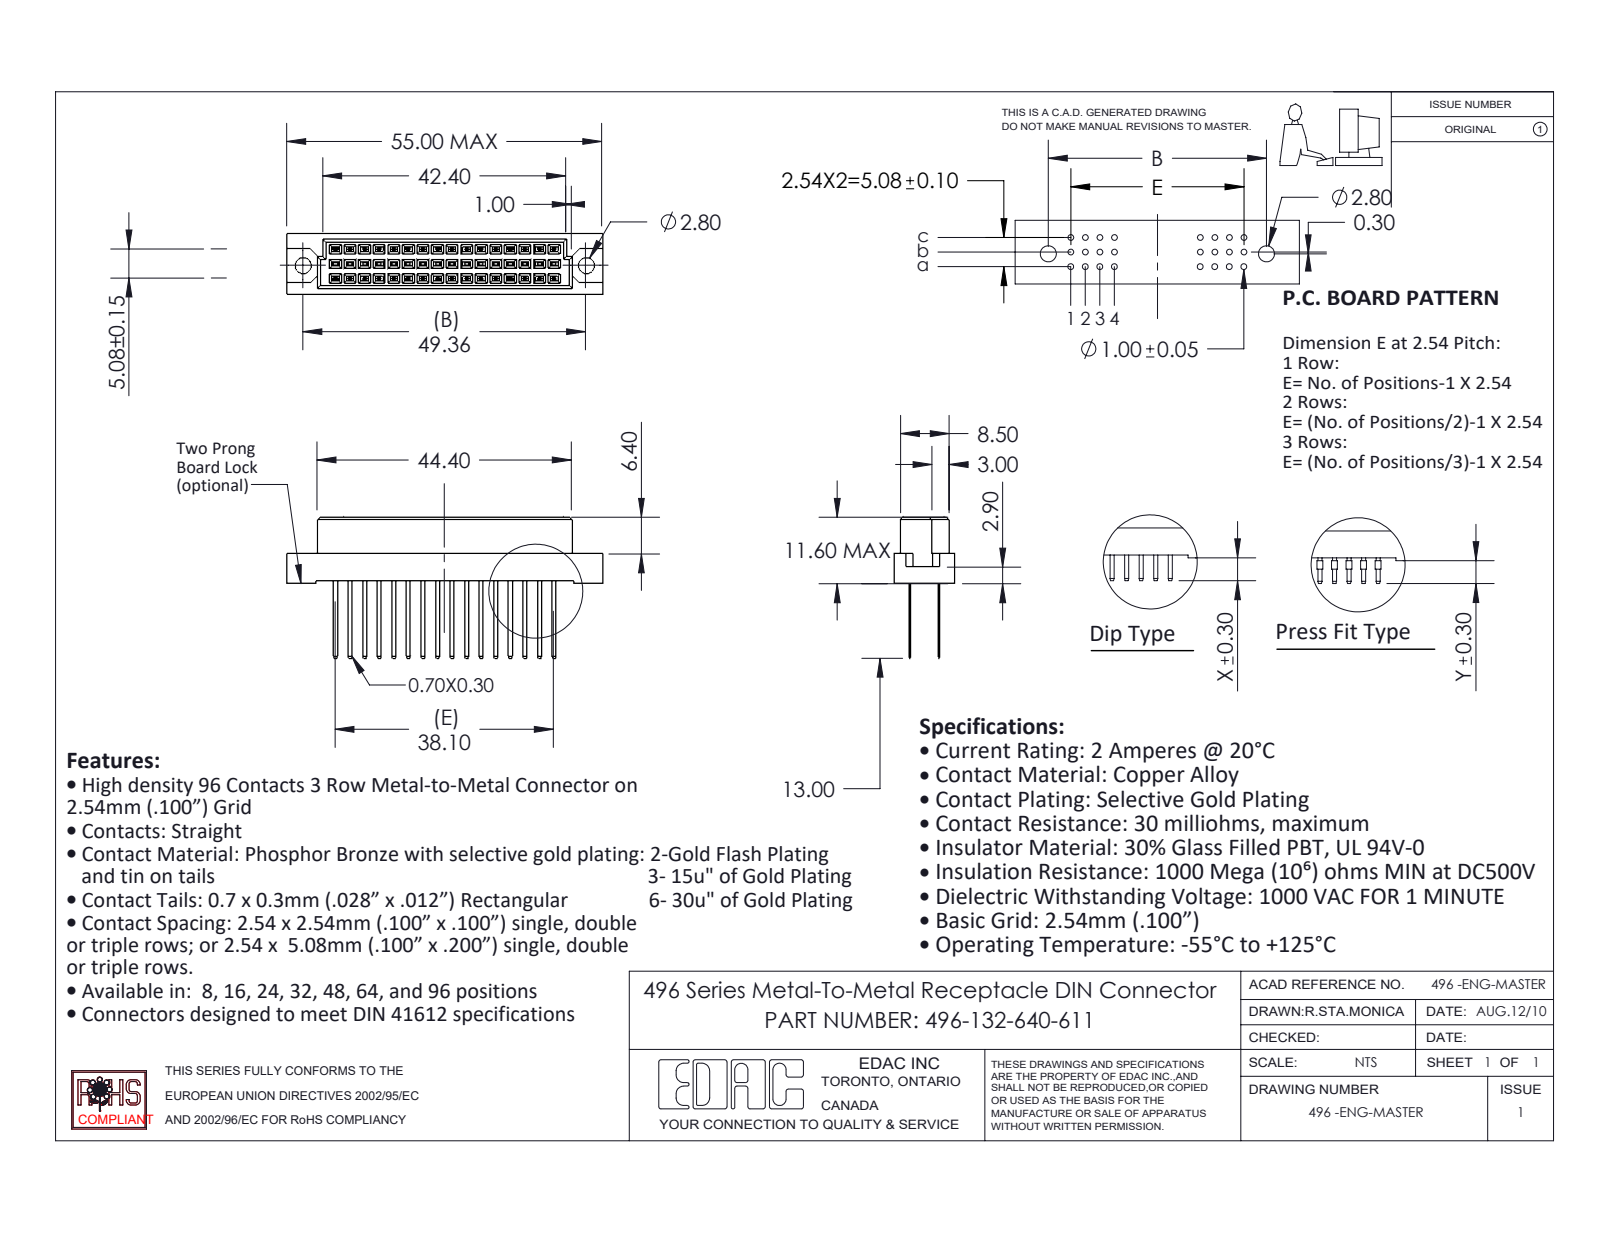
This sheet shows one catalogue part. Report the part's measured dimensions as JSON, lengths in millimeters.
{"part_name": "496 Part_48; 496-290_40; 496-132-640-611", "step_written_by": "SolidWorks 2020 (CONFIG_CONTROL_DESIGN)", "units": "millimeters", "bodies": {"solids": 33, "faces": 986, "planar": 982, "cylindrical": 4, "other": 0}, "overall_size": [55, 24.6, 10.6], "volume_mm3": 4705, "surface_area_mm2": 5324, "round_holes": [[2.8, 2]], "face_to_face_distances": [5.08, 2.54, 1.05, 9.55, 2.61, 2.91, 7.69, 7.99, 1.56, 1.86], "hole_center_spacings": [49.36]}
